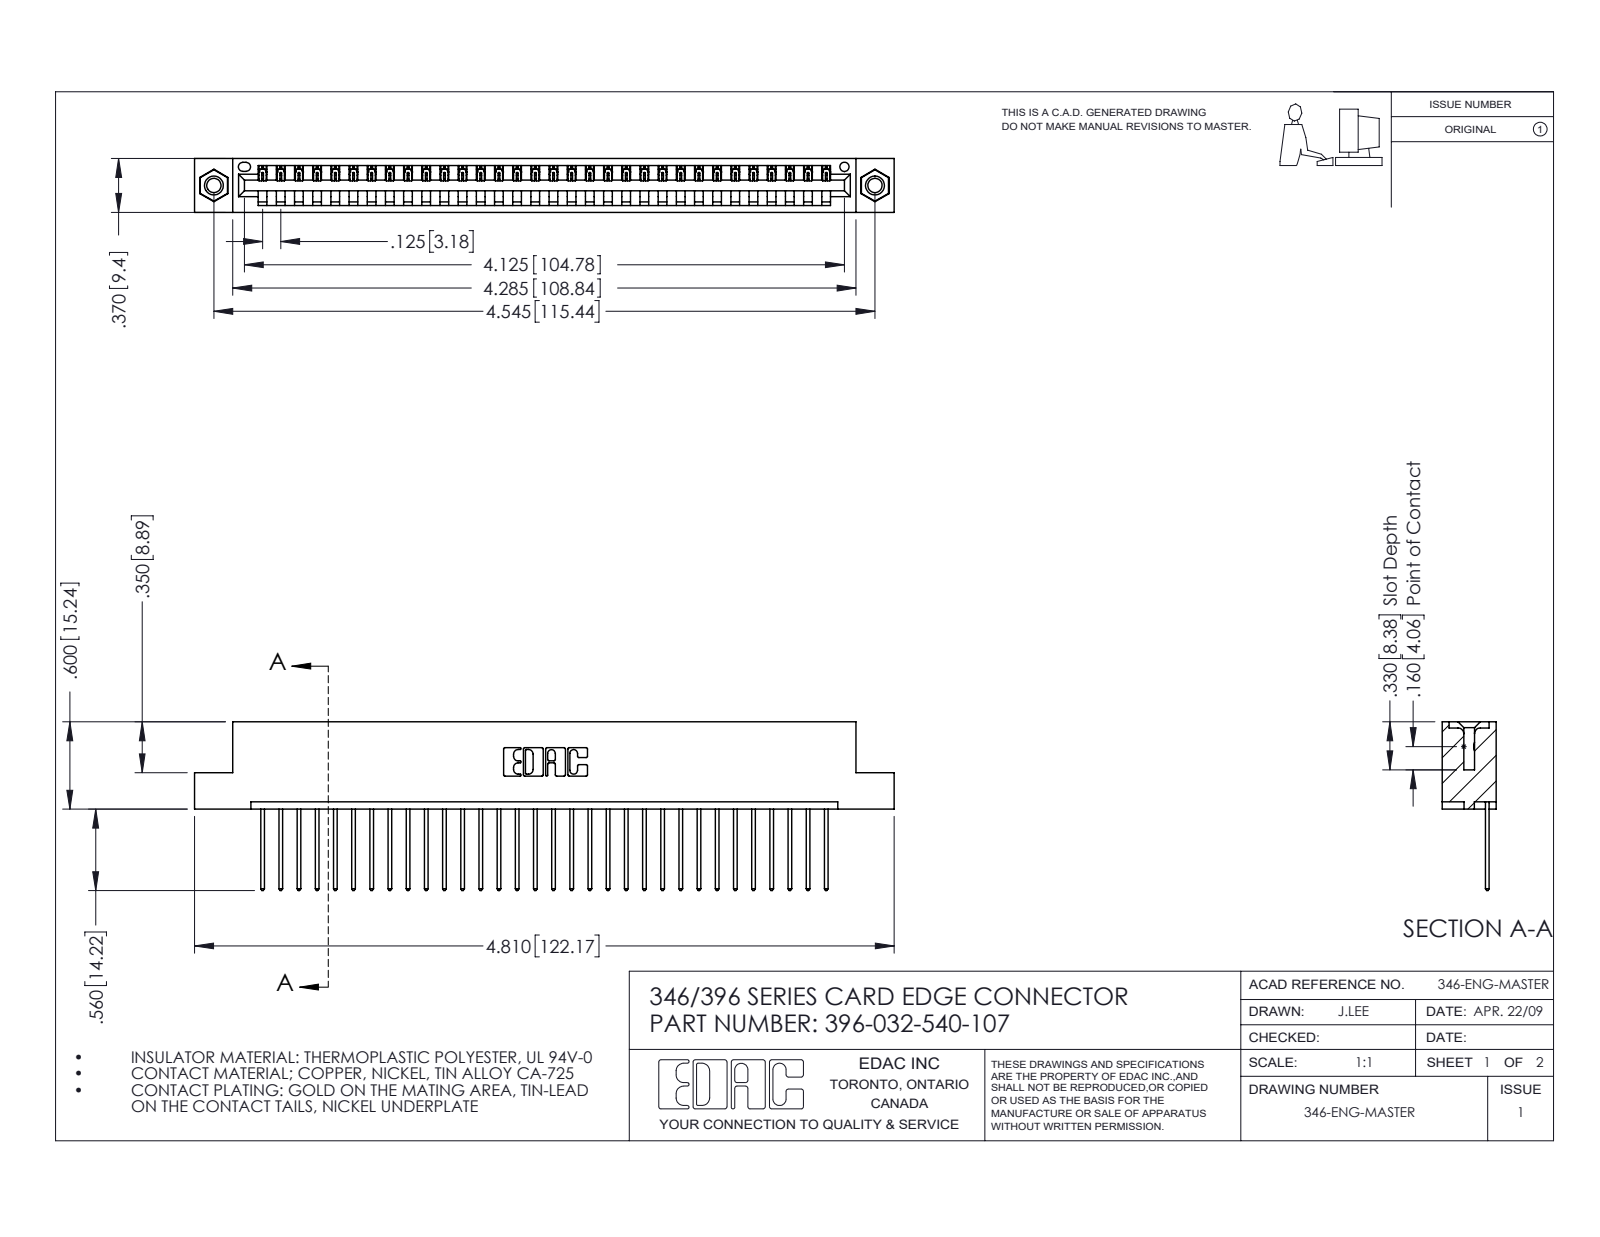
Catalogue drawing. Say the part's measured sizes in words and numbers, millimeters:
The part is named "345-292-001_345-293-140; 346 Part_Flush Mounting Lugs - 0.156 Dia-TI; 396-032-540-107; 345-250-001_345-250-005-103". Its 3-D file was written by "SolidWorks 2016 (CONFIG_CONTROL_DESIGN)". It is 35 solids with 2038 faces: 1388 planar, 634 cylindrical and 16 other. Overall it measures 122.2 by 29.5 by 9.4 millimeters. Its volume is 11 700 cubic millimeters and its surface area 14 810 square millimeters. Round holes: 2 of diameter 2.5, 2 of diameter 3.2, 2 of diameter 4, 1 of diameter 1.6. Round bosses or shafts: 2 of diameter 3.9. Partial cylindrical surfaces (rounded edges, fillets, slot ends): 64 of radius 0.2, 64 of radius 0.3, 22 of radius 0.3, 6 of radius 0.2, 6 of radius 0.8, 3 of radius 0.7, 2 of radius 0.8, 2 of radius 1. The main face-to-face distances are 1.2, 8.2, 9.4, 6.4, 1.8, 7.6, 0.6, 3.8, 5.6, 2.5. The hole center spacings are 6.2, 110.2, 115.4.
